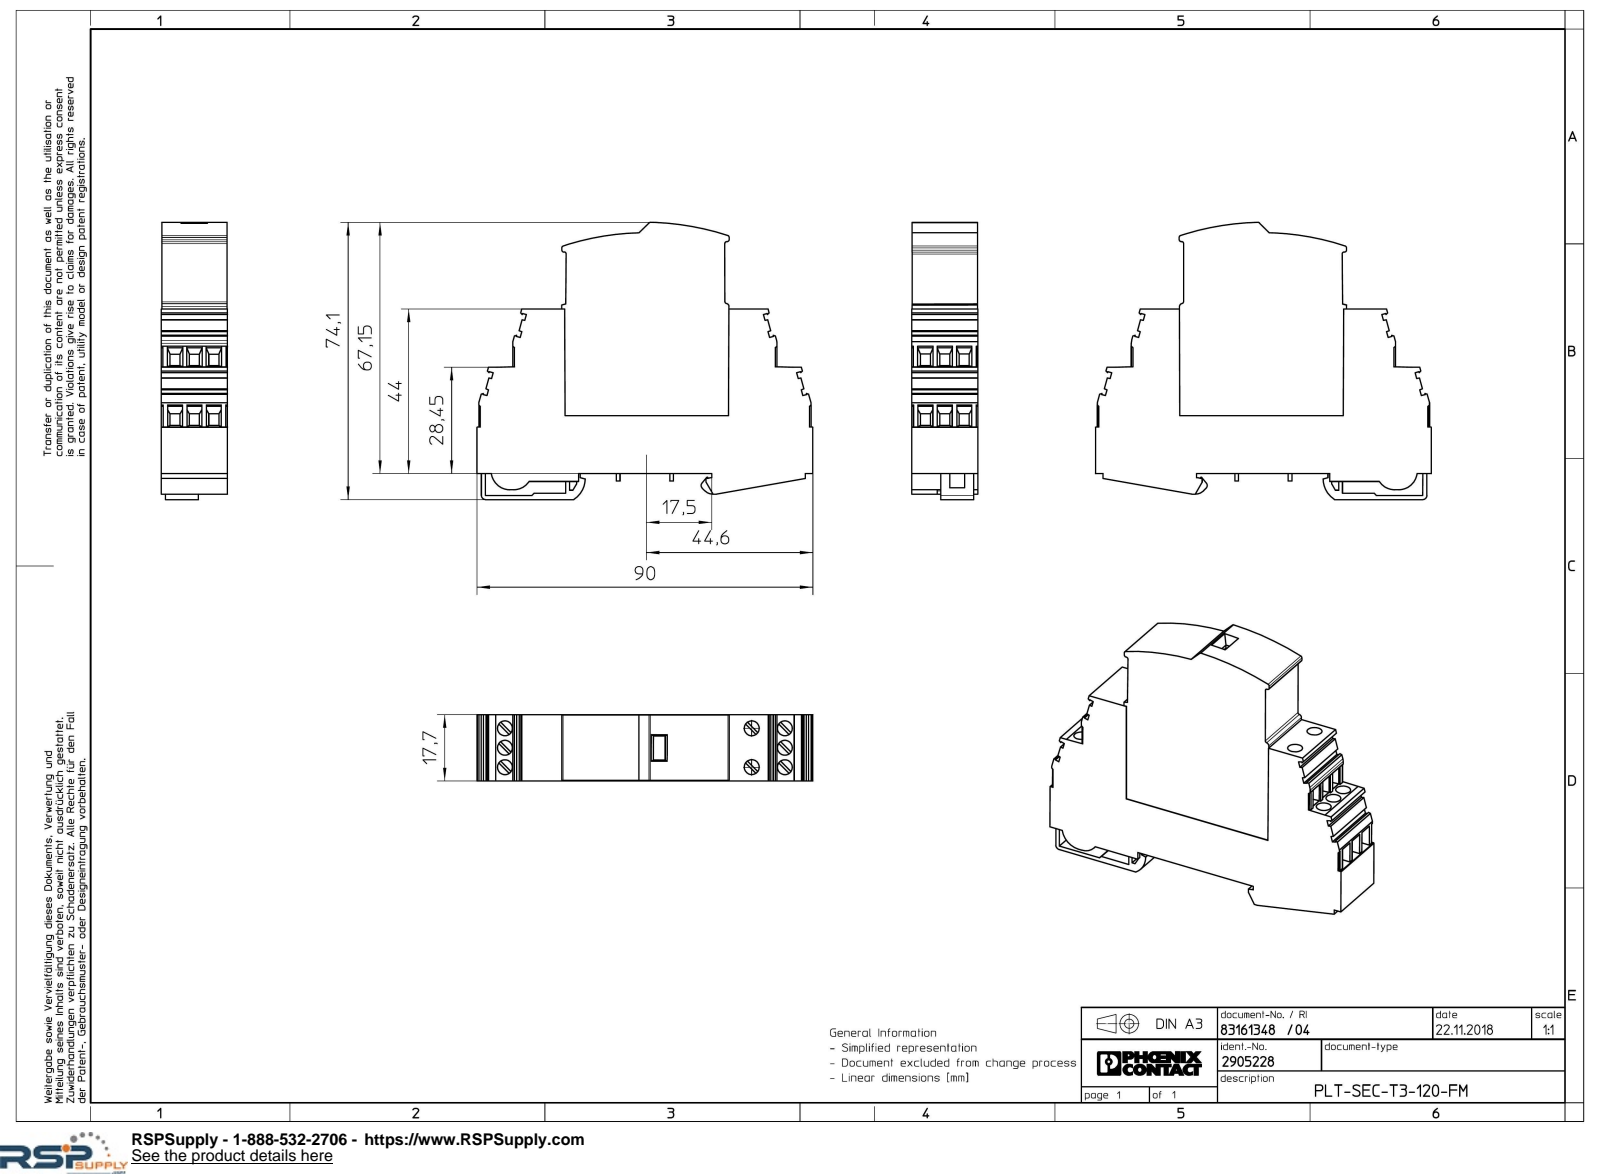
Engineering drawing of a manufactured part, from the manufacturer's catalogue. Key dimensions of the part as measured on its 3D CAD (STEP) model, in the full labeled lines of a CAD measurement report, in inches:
Part name (STEP PRODUCT): PLT_SEC_T3_230_FM-select
STEP written by: Creo Elements/Direct Modeling 20.1A 29-Sep-2018 (C) Parametric Technology GmbH (AUTOMOTIVE_DESIGN)
Units: inches
Bodies: 1 solid, 418 faces (382 planar, 23 cylindrical, 13 other)
Overall size (bounding box): 3.543 × 2.917 × 0.697
Volume: 4.909 in³ · Surface area: 26.65 in²
Round holes (diameter × count): ⌀0.157 ×2
Partial cylindrical surfaces — rounded edges, fillets, slot ends (radius × count): R0.02 ×8, R0.118 ×2, R0.197 ×2, R0.008 ×1, R0.03 ×1, R0.039 ×1, R0.043 ×1, R0.256 ×1
Main face-to-face distances: 0.693, 0.697, 0.689, 1.732, 0.176, 0.083, 1.815, 3.543, 0.03, 0.191
Hole centre spacings: 0.409
